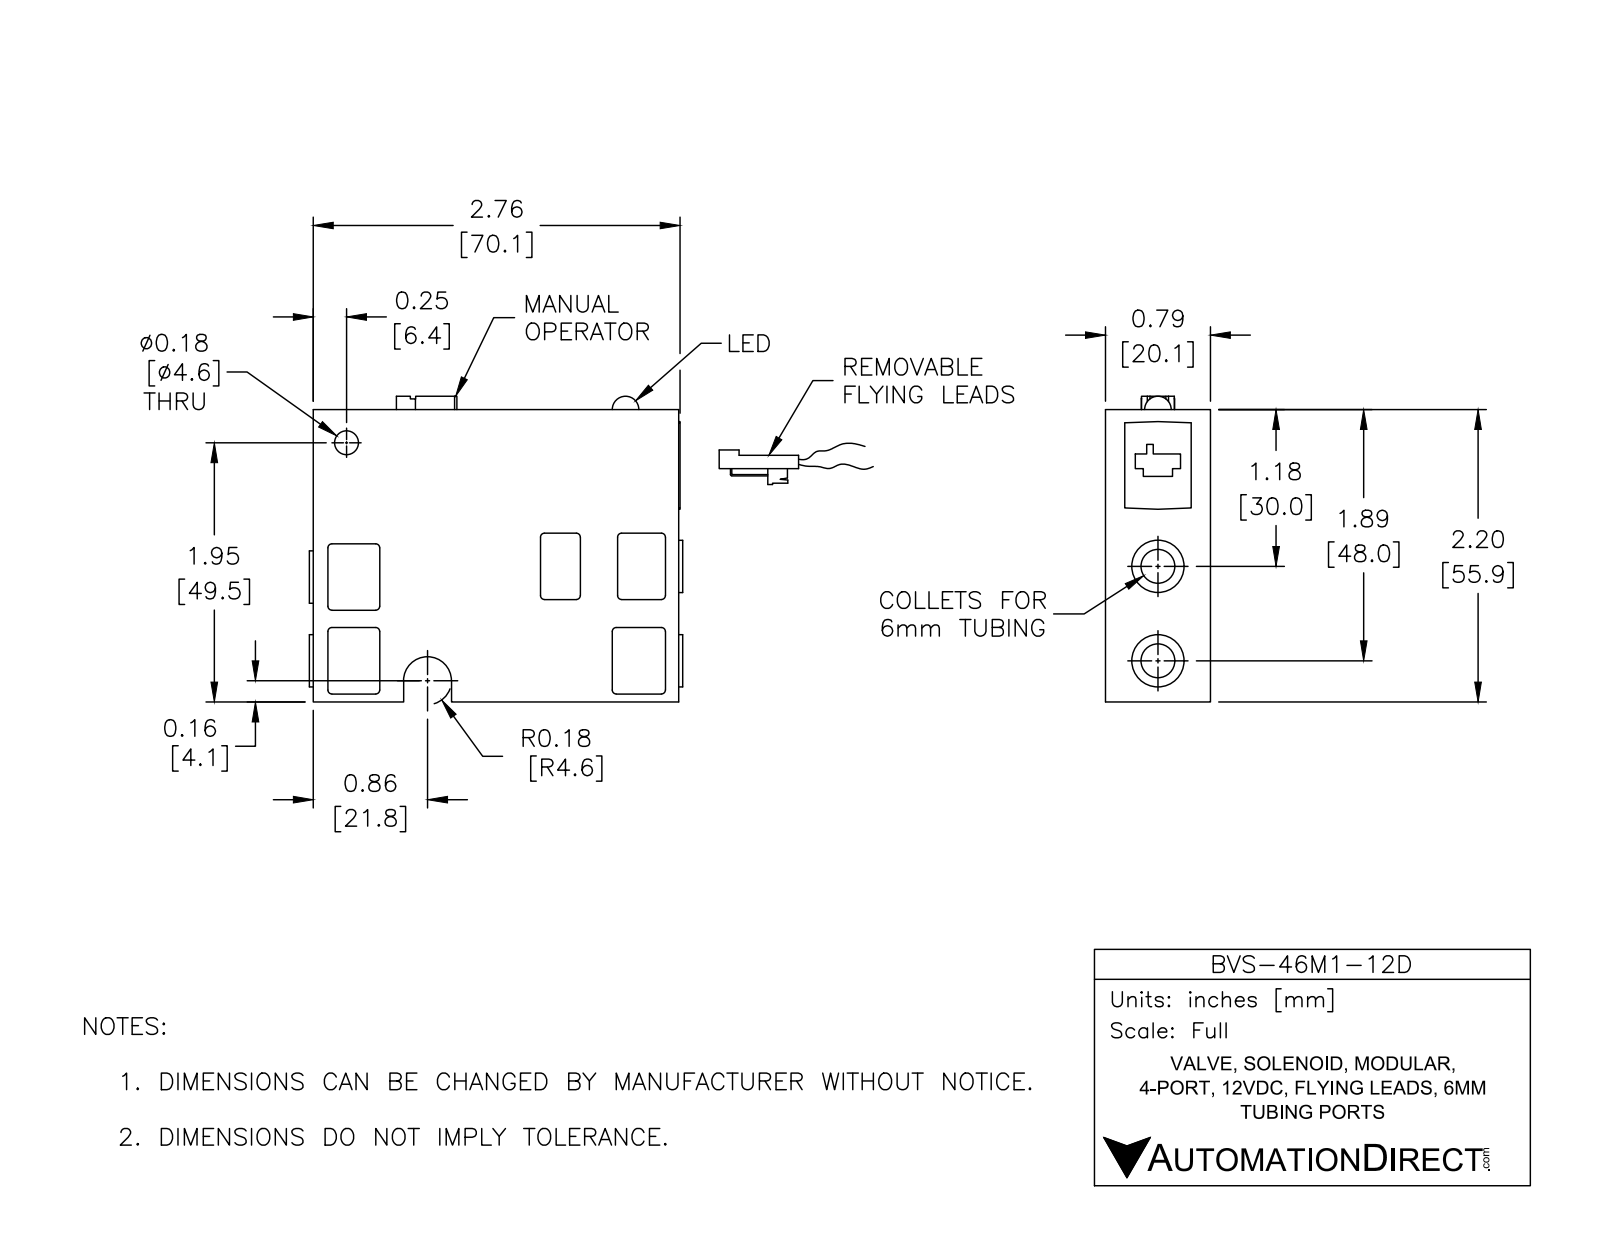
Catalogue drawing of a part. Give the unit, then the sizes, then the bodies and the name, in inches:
Units: inches
Overall size (bounding box): 3.009 × 2.3 × 0.79
Round holes (diameter × count): ⌀0.25 ×3, ⌀0.1 ×1, ⌀0.18 ×1
Round bosses / shafts (diameter × count): ⌀0.06 ×6, ⌀0.394 ×3
Partial cylindrical surfaces — rounded edges, fillets, slot ends (radius × count): R0.03 ×20, R0.02 ×2, R0.125 ×1, R0.18 ×1
Main face-to-face distances: 0.79, 0.1, 2.2, 0.69, 2.75, 0.59, 0.5, 0.11, 2.65, 2.76
Hole centre spacings: 0.08, 0.55, 0.63, 0.63, 0.71, 1.26
Volume: 4.377 in³ · Surface area: 25.04 in²
Bodies: 1 solid, 173 faces (85 planar, 78 cylindrical, 10 other)
Part name (STEP PRODUCT): BVS-46M1-12D
STEP written by: SolidWorks 2016 (AUTOMOTIVE_DESIGN)
